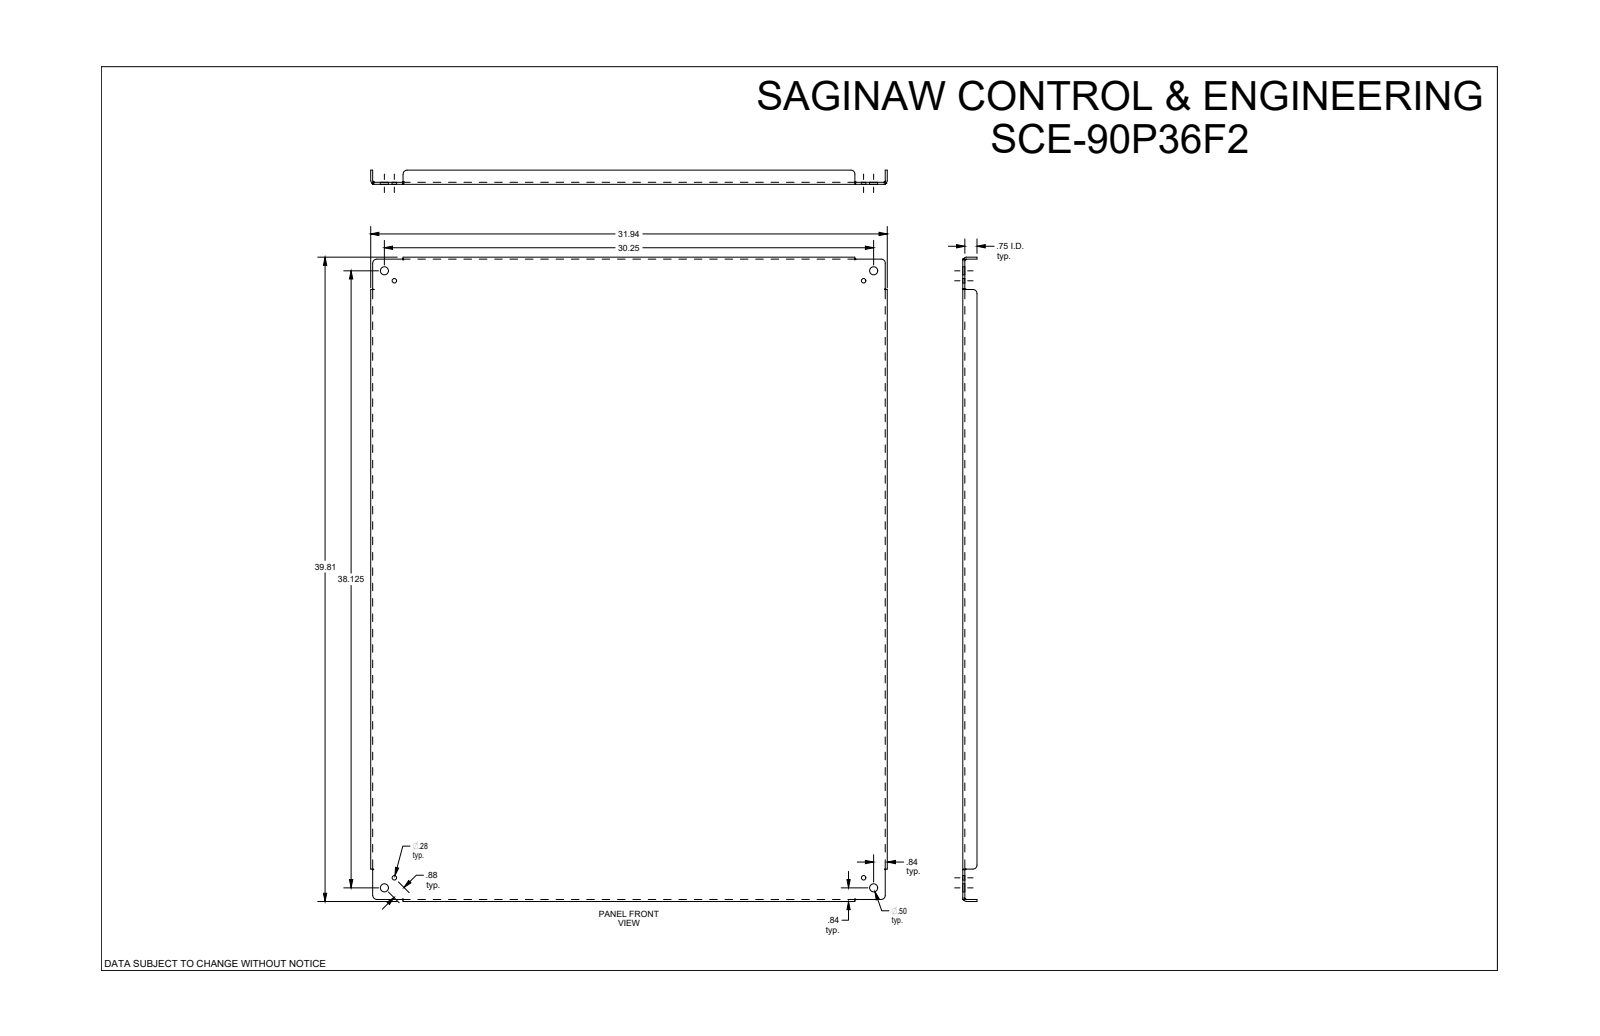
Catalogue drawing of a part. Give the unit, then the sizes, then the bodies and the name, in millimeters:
Units: millimetres
Overall size (bounding box): 1011.3 × 811.2 × 22.2
Round holes (diameter × count): ⌀7.1 ×4, ⌀12.7 ×4
Partial cylindrical surfaces — rounded edges, fillets, slot ends (radius × count): R6.4 ×8, R2.8 ×4, R6 ×4
Main face-to-face distances: 3.2, 3.2, 808.1, 1008, 804.8, 811.2, 1004.9, 1011.3, 19.1, 22.2
Hole centre spacings: 22.2, 752.8, 952.8, 1214.1, 736.9, 768.4, 936.9, 968.4
Volume: 2 774 000 mm³ · Surface area: 1 761 000 mm²
Bodies: 1 solid, 82 faces (30 planar, 28 cylindrical, 24 other)
Part name (STEP PRODUCT): SCE-90P36F2
STEP written by: SolidWorks 2019 (AUTOMOTIVE_DESIGN)
